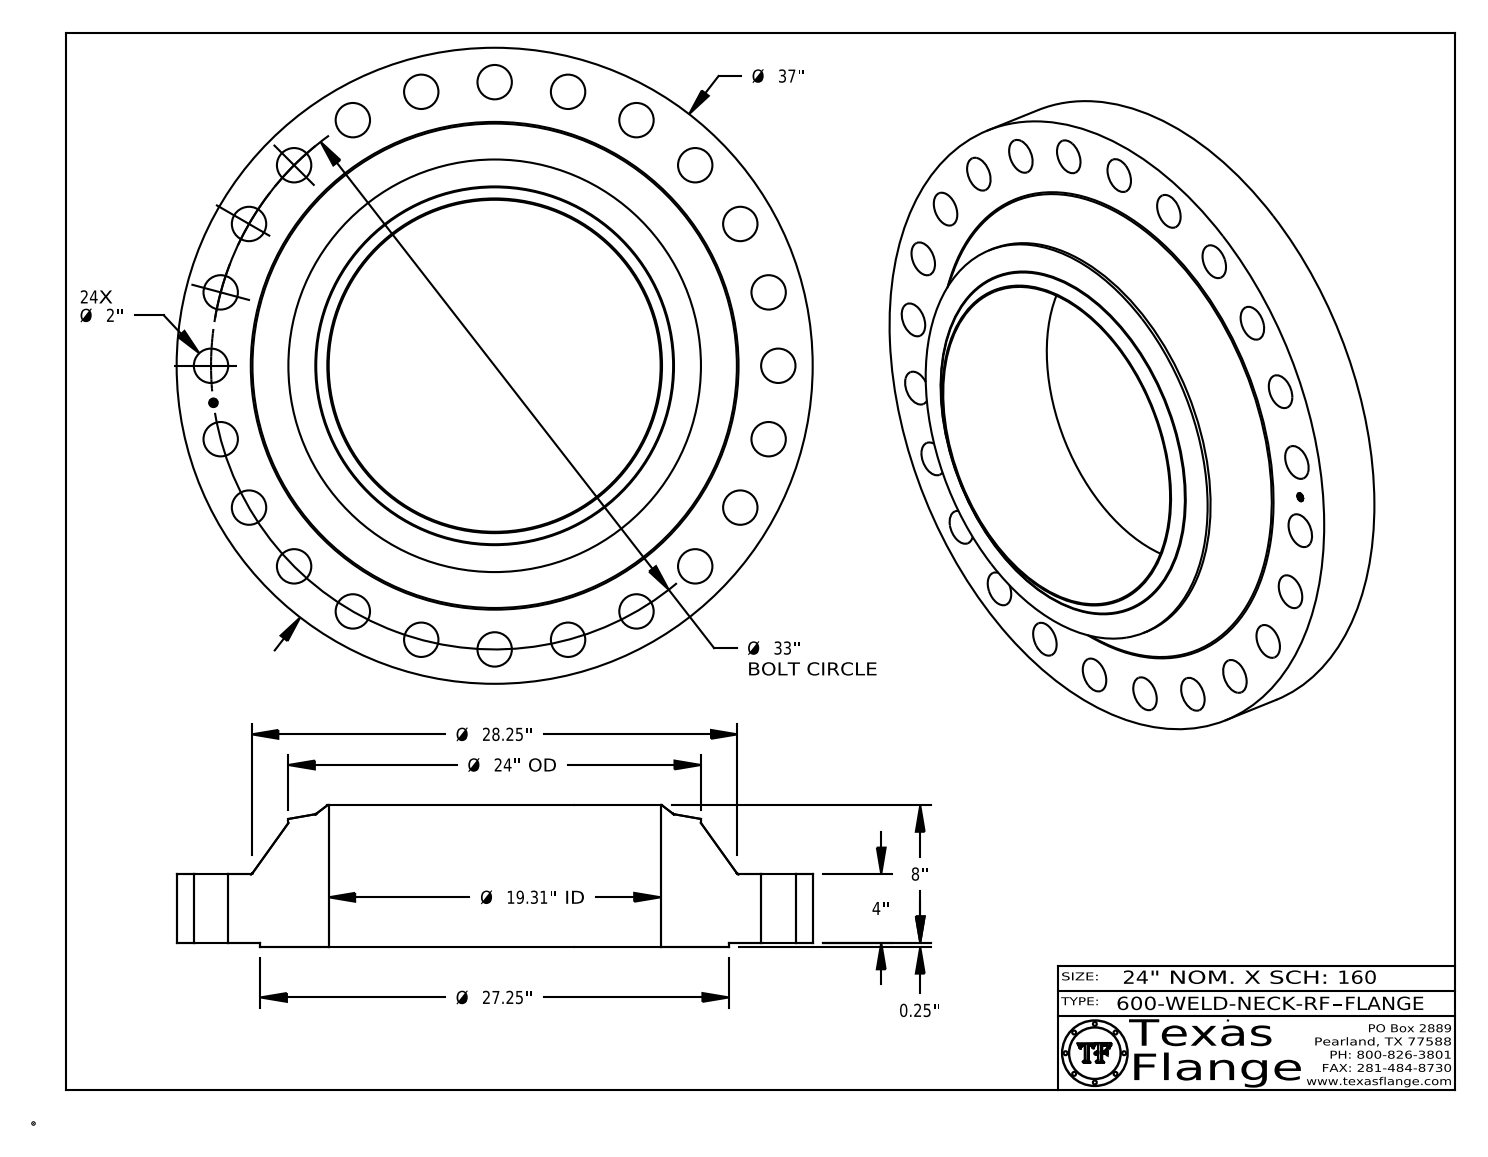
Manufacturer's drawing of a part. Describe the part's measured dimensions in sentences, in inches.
The part is named "600-WELD-NECK-RF". Its 3-D file was written by "CATIA V5 STEP AP214 (AUTOMOTIVE_DESIGN)". It is 1 solid with 455 faces: 369 planar, 76 cylindrical and 10 other. Overall it measures 37 by 37 by 8.25 inches. Its volume is 3 705 cubic inches and its surface area 3 159 square inches. Round holes: 24 of diameter 2, 1 of diameter 0.495, 1 of diameter 19.312. Round bosses or shafts: 8 of diameter 0.03, 1 of diameter 37, 1 of diameter 27.25, 1 of diameter 24, 1 of diameter 0.39. The main face-to-face distances are 4, 0.25, 4.25, 8.25, 8, 0.015, 4.235, 3.985, 4.015, 0.07. The hole center spacings are 16.5, 4.307, 8.541, 20.089, 23.335, 26.181, 31.876, 32.718.
